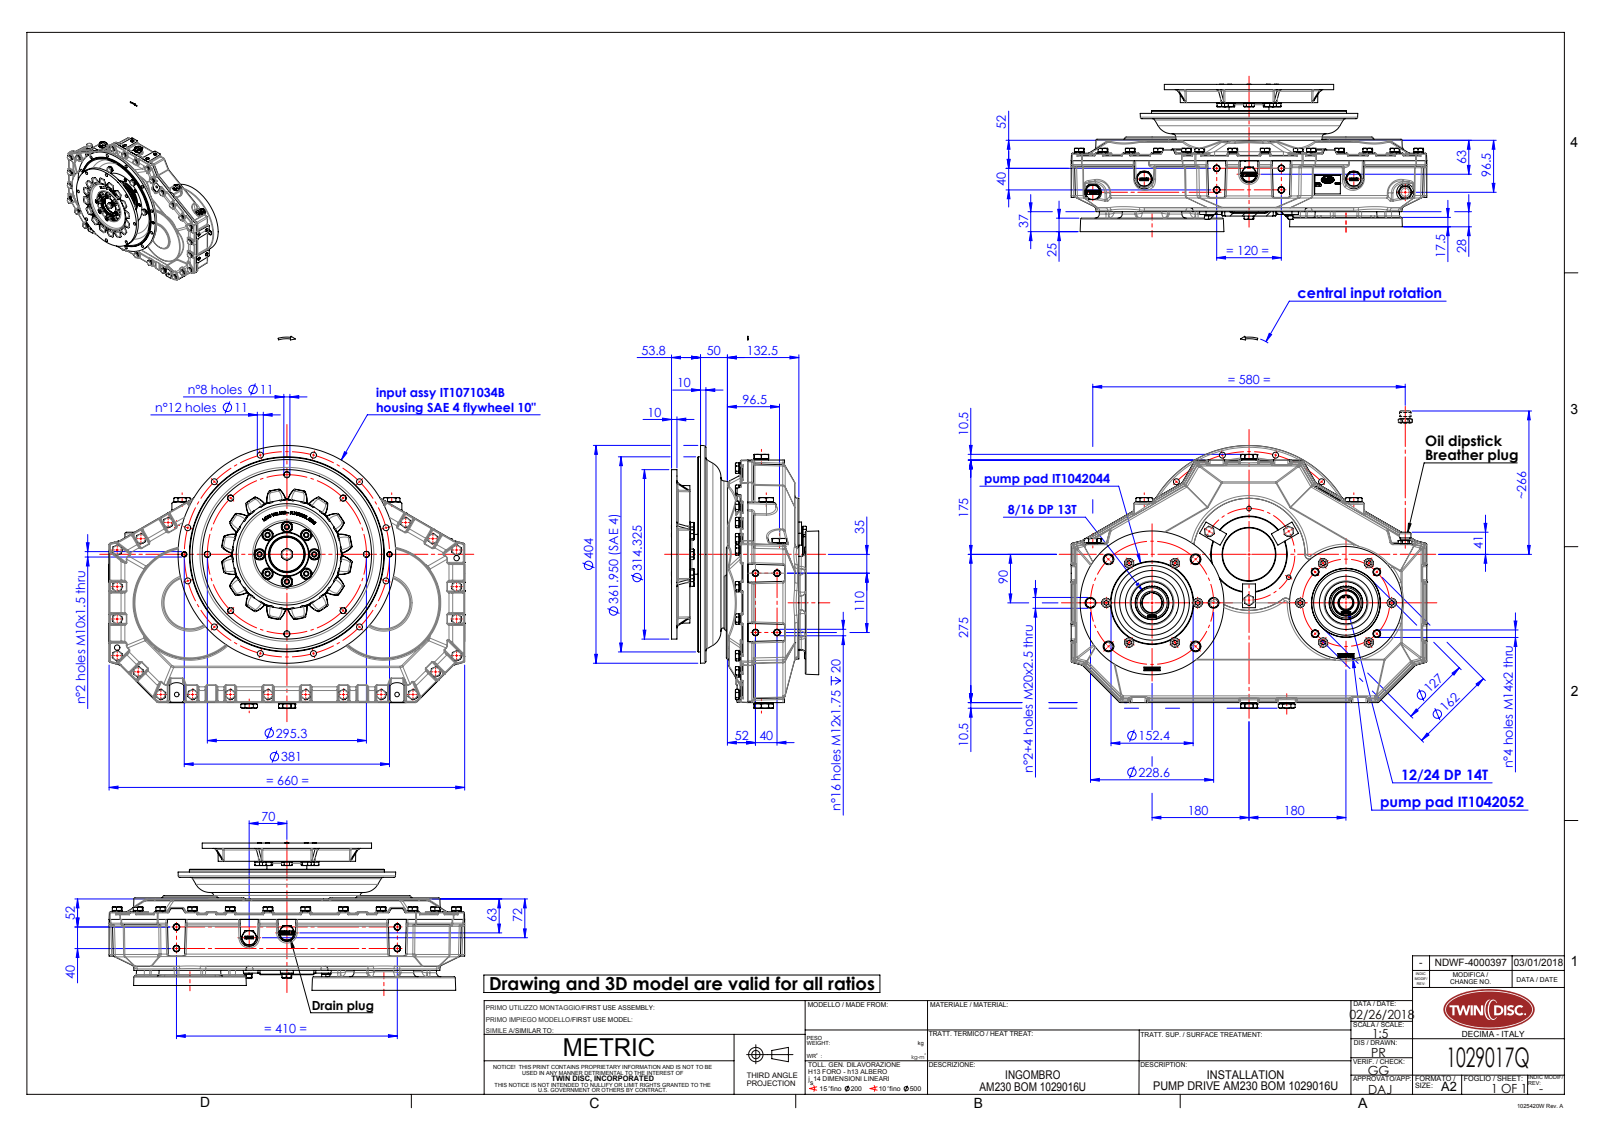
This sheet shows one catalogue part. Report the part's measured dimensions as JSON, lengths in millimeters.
{"part_name": "IT2021216_rev03-installation; IT4588040_rev00-installation; ITam230-002_rev00-installation; ITam230-001_rev01-installation (+6 more)", "step_written_by": "SolidWorks 2015 (AUTOMOTIVE_DESIGN)", "units": "millimeters", "bodies": {"solids": 39, "faces": 8339, "planar": 3520, "cylindrical": 2114, "other": 2705}, "overall_size": [690.04, 660, 273.5], "volume_mm3": 6493000, "surface_area_mm2": 3111000, "round_holes": [[10.5, 48], [10.2, 41], [8.5, 32], [11, 27], [12, 16], [17, 12], [10, 10], [10.7, 8], [12.2, 7], [13, 7], [17.5, 6], [14, 4]], "round_bosses_or_shafts": [[10, 55], [16.2, 41], [18.1, 32], [16, 12], [21, 8], [21.1, 7], [20, 7], [18, 7]], "partial_cylinders_radius": [[2, 217], [3, 147], [2.5, 110], [5, 90], [1, 64], [4, 64], [0.45, 58], [42.91, 32]], "face_to_face_distances": [40, 21, 94.5, 38, 132.5, 37, 152.5, 10, 5, 19], "hole_center_spacings": [120, 57.4, 75, 138.58, 40, 207.84, 22.59, 51.37]}
